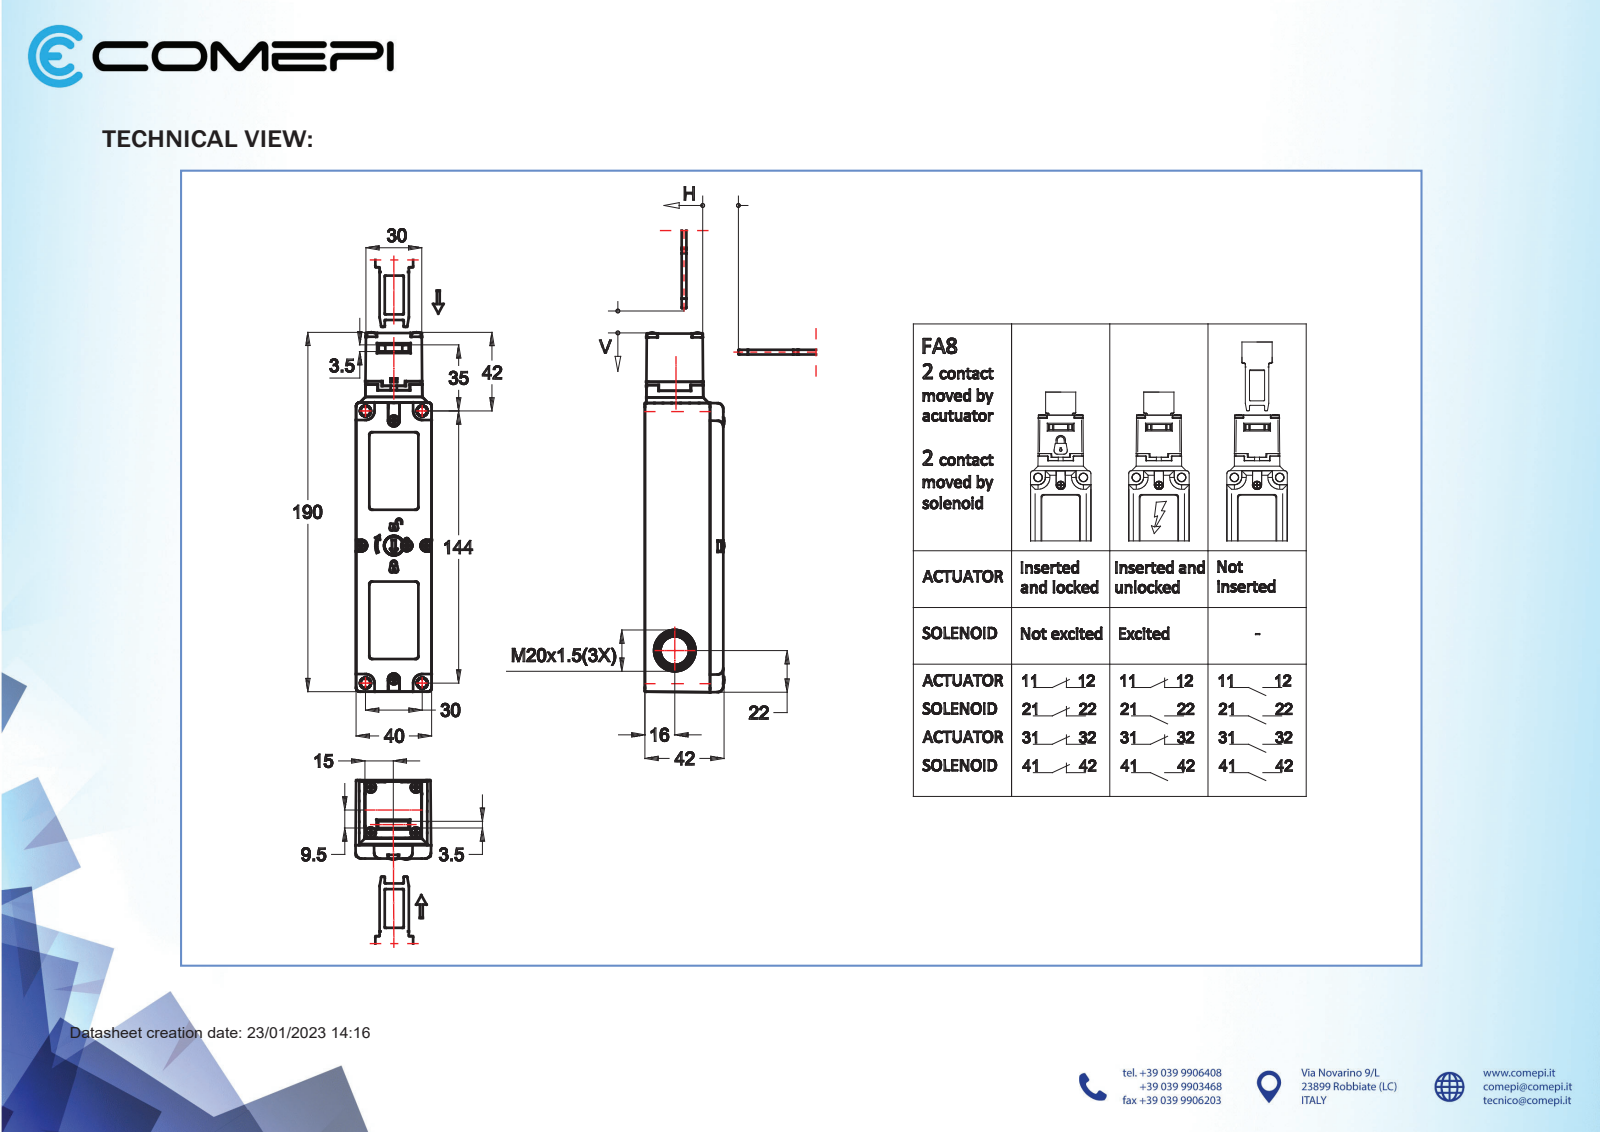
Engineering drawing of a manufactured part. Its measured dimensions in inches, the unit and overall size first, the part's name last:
Units: inches
Overall size (bounding box): 7.485 × 1.649 × 1.575
Round holes (diameter × count): ⌀0.098 ×4, ⌀0.861 ×2, ⌀0.059 ×1, ⌀0.274 ×1, ⌀0.394 ×1, ⌀0.472 ×1, ⌀0.669 ×1, ⌀0.799 ×1, ⌀0.811 ×1, ⌀0.812 ×1, ⌀0.945 ×1, ⌀0.984 ×1
Round bosses / shafts (diameter × count): ⌀0.114 ×9, ⌀0.033 ×2, ⌀0.953 ×1, ⌀0.268 ×1, ⌀0.26 ×1, ⌀0.169 ×1
Partial cylindrical surfaces — rounded edges, fillets, slot ends (radius × count): R0.008 ×86, R0.039 ×22, R0.02 ×16, R0.118 ×16, R0.005 ×13, R0.012 ×11, R0.059 ×10, R0.009 ×4
Main face-to-face distances: 0.091, 1.378, 0.098, 1.181, 0.071, 0.157, 1.307, 1.535, 1.465, 0.083
Hole centre spacings: 0.677, 2.695, 2.867, 0.335, 1.354, 2.608, 2.785, 5.394
Volume: 12.73 in³ · Surface area: 159.5 in²
Bodies: 14 solids, 1964 faces (1095 planar, 301 cylindrical, 568 other)
Part name (STEP PRODUCT): FEP5KP1FA8-024M
STEP written by: SolidWorks 2021 (AUTOMOTIVE_DESIGN)
